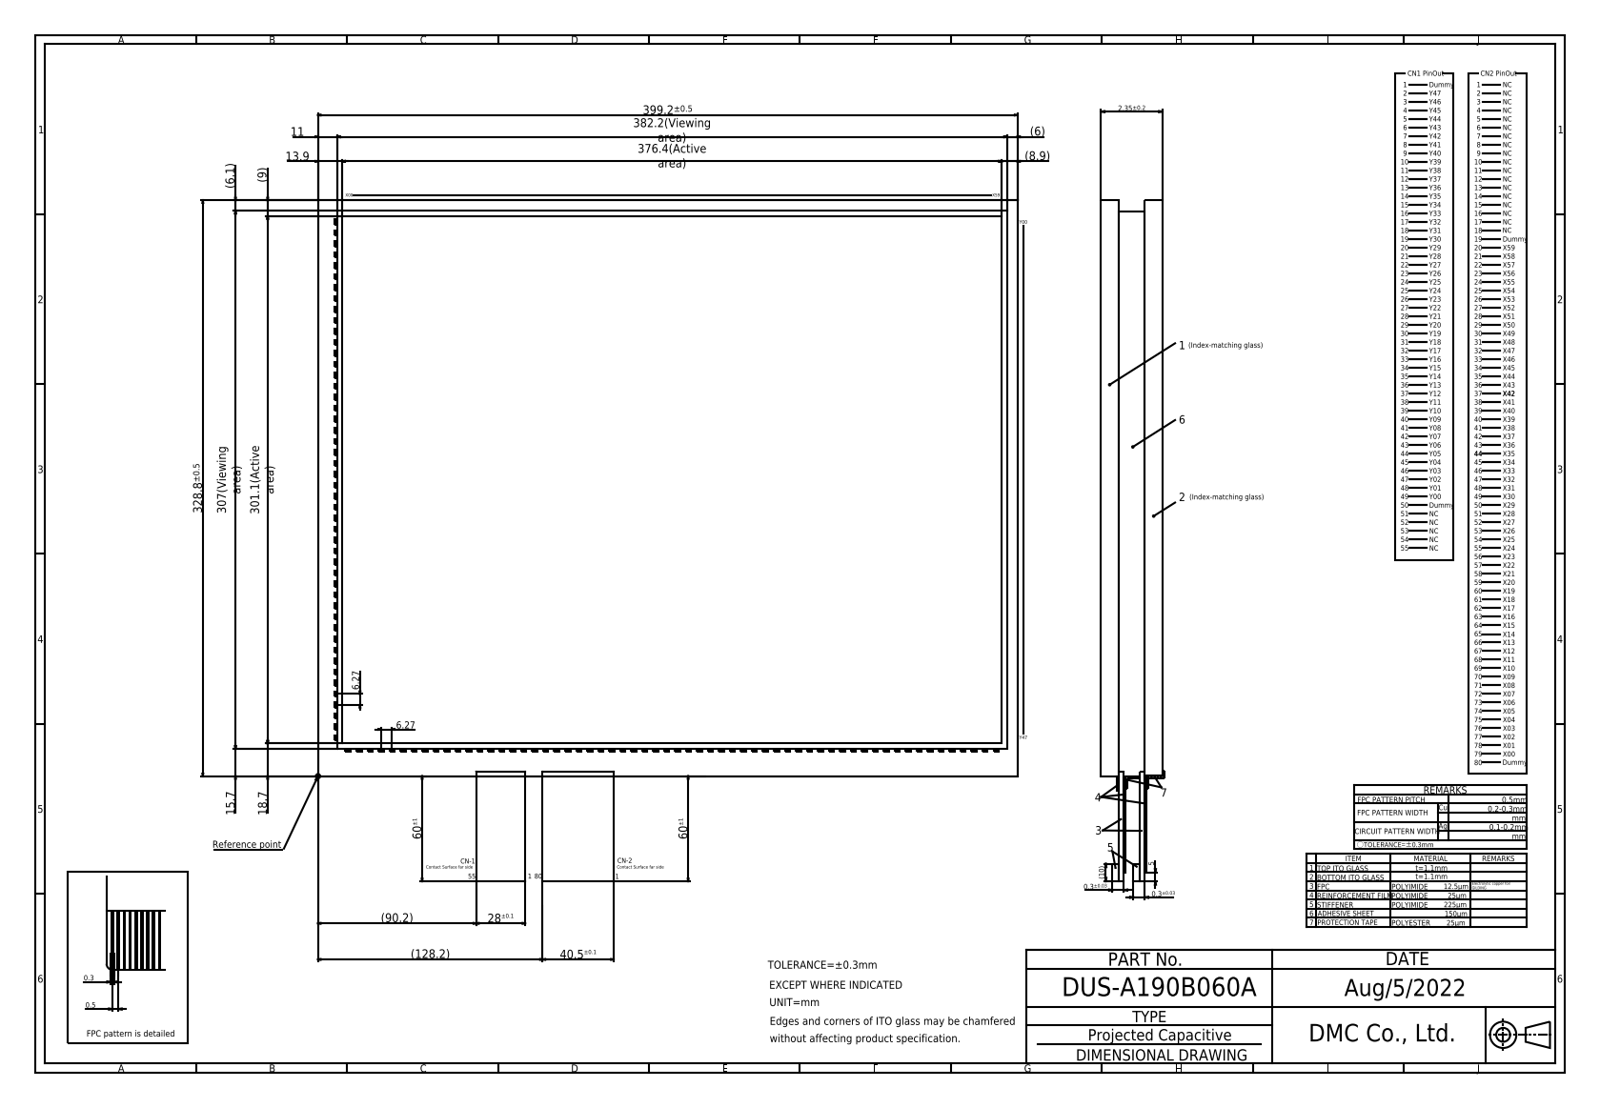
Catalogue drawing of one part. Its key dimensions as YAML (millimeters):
part_name: "DUS-A190B060A"
step_written_by: "Autodesk Inventor 2020 (CONFIG_CONTROL_DESIGN)"
units: millimeters
bodies: {solids: 1, faces: 578, planar: 574, cylindrical: 4, other: 0}
overall_size: [558.88, 460.32, 2.35]
volume: 308635
surface_area: 274517
partial_cylinders:
  - {radius: 0.2, count: 4}
face_to_face_distances: [2.35, 1.1, 2.25, 1.2, 1.15, 1, 1.25, 328.8, 399.2, 0.8]
